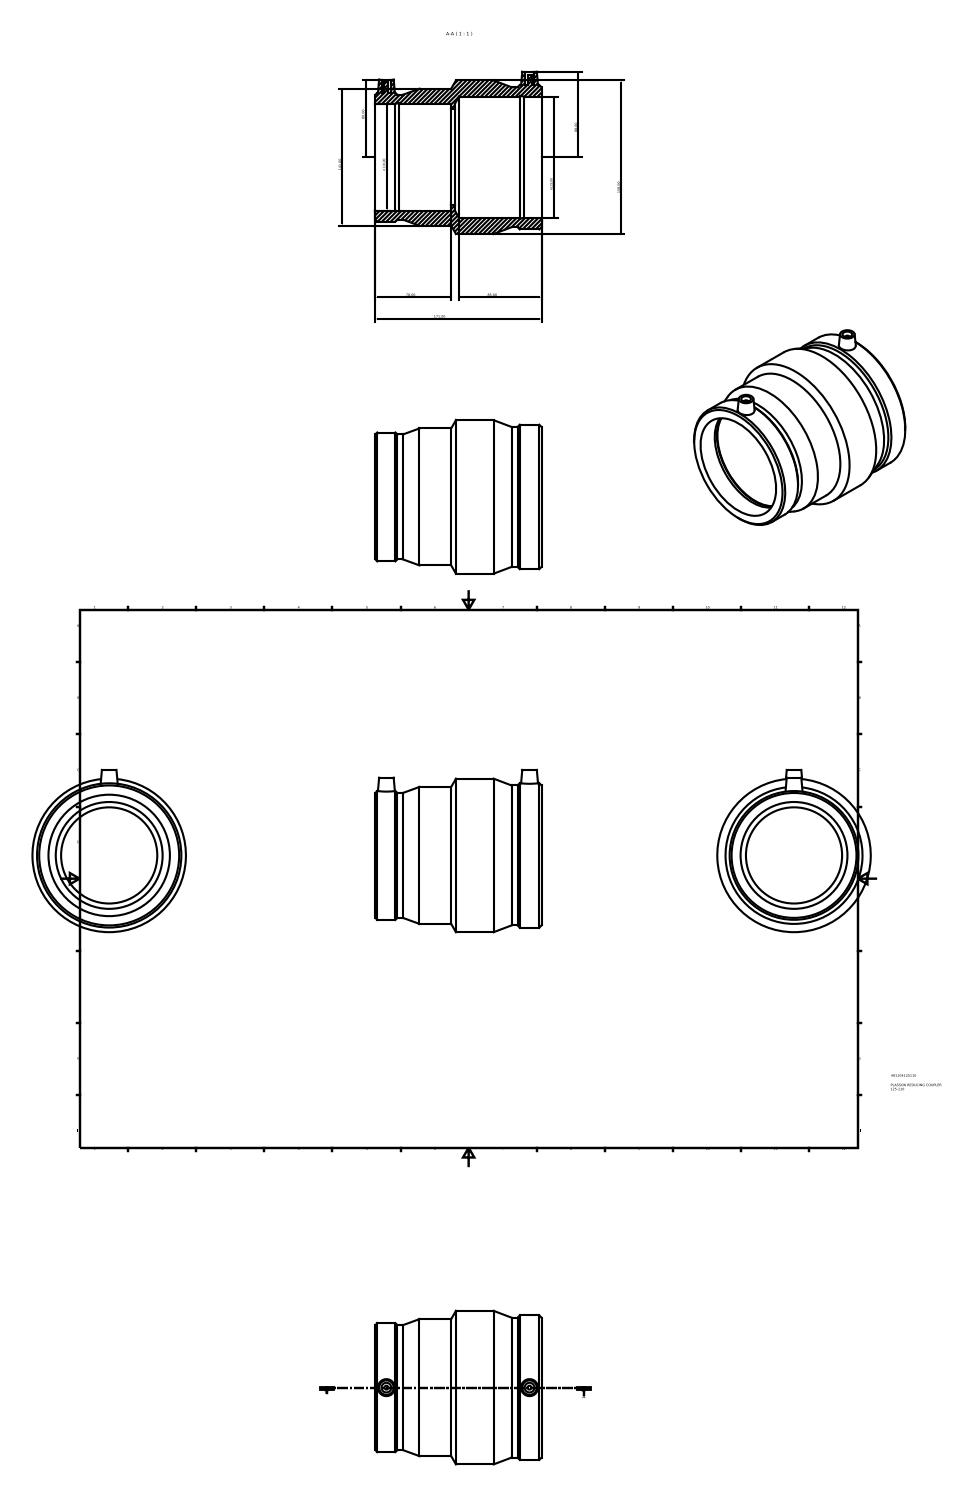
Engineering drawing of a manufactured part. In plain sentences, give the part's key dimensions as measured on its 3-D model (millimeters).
The part is named "491104125110". Its 3-D file was written by "Autodesk Inventor 2015 (AUTOMOTIVE_DESIGN)". It is 1 solid with 39 faces: 12 planar, 15 cylindrical and 12 other. Overall it measures 171 by 167 by 158 millimeters. Its volume is 984 690 cubic millimeters and its surface area 161 844 square millimeters. Round holes: 2 of diameter 10, 1 of diameter 99, 1 of diameter 110, 1 of diameter 125. Round bosses or shafts: 2 of diameter 4, 1 of diameter 158, 1 of diameter 148.52, 1 of diameter 144.06, 1 of diameter 141, 1 of diameter 132.54, 1 of diameter 128.56. The main face-to-face distances are 171, 81.9, 89.1, 78, 3.9, 93, 148.58, 70.58, 66.68, 22.42. The hole center spacings are 147.36.
